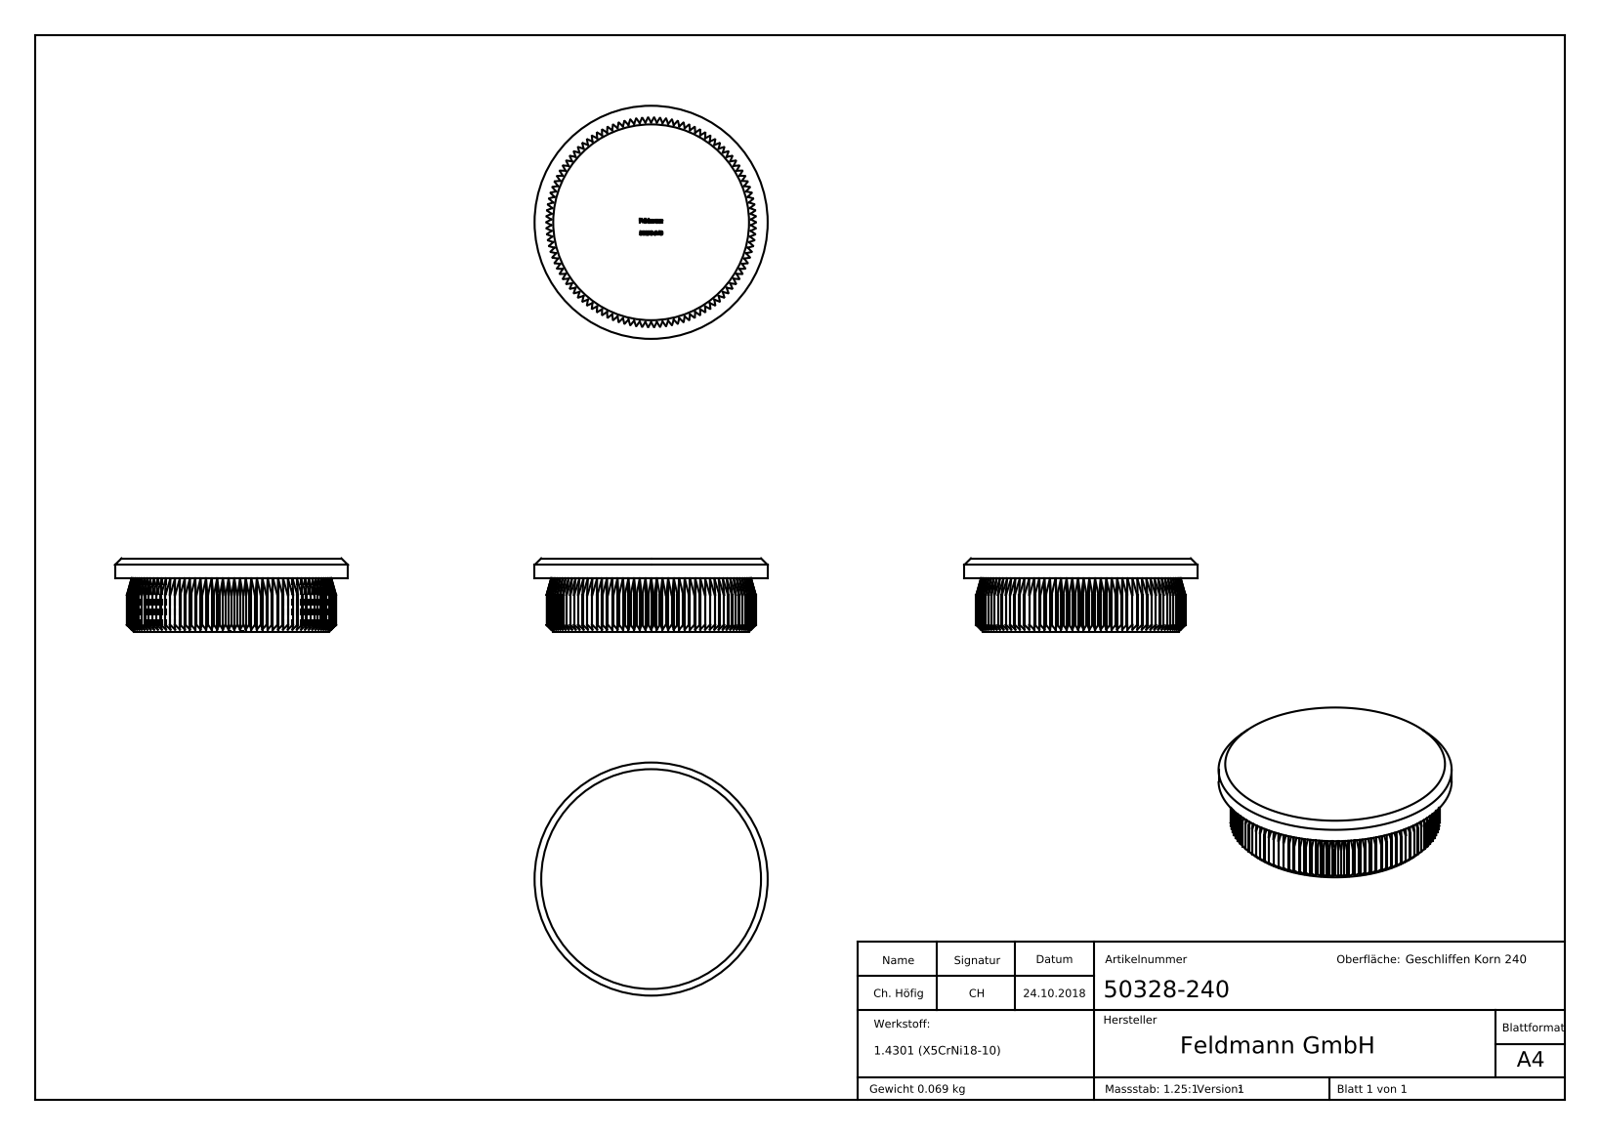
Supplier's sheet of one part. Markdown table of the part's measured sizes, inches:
| quantity | value |
| --- | --- |
| part name | 50328-240 |
| STEP written by | SolidWorks 2015 (CONFIG_CONTROL_DESIGN) |
| units | inches |
| bodies | 1 solid, 702 faces (361 planar, 112 cylindrical, 229 other) |
| overall size | 1.378 × 1.378 × 0.433 |
| volume | 0.532 in³ |
| surface area | 5.45 in² |
| round bosses / shafts (diameter × count) | 1.378 × 1 |
| partial cylindrical surfaces (radius × count) | 0.618 × 1 |
| main face-to-face distances | 0.433, 0.591, 0.315, 0.118, 0.591, 0.59, 0.311, 0.429, 0.065, 0.072 |
